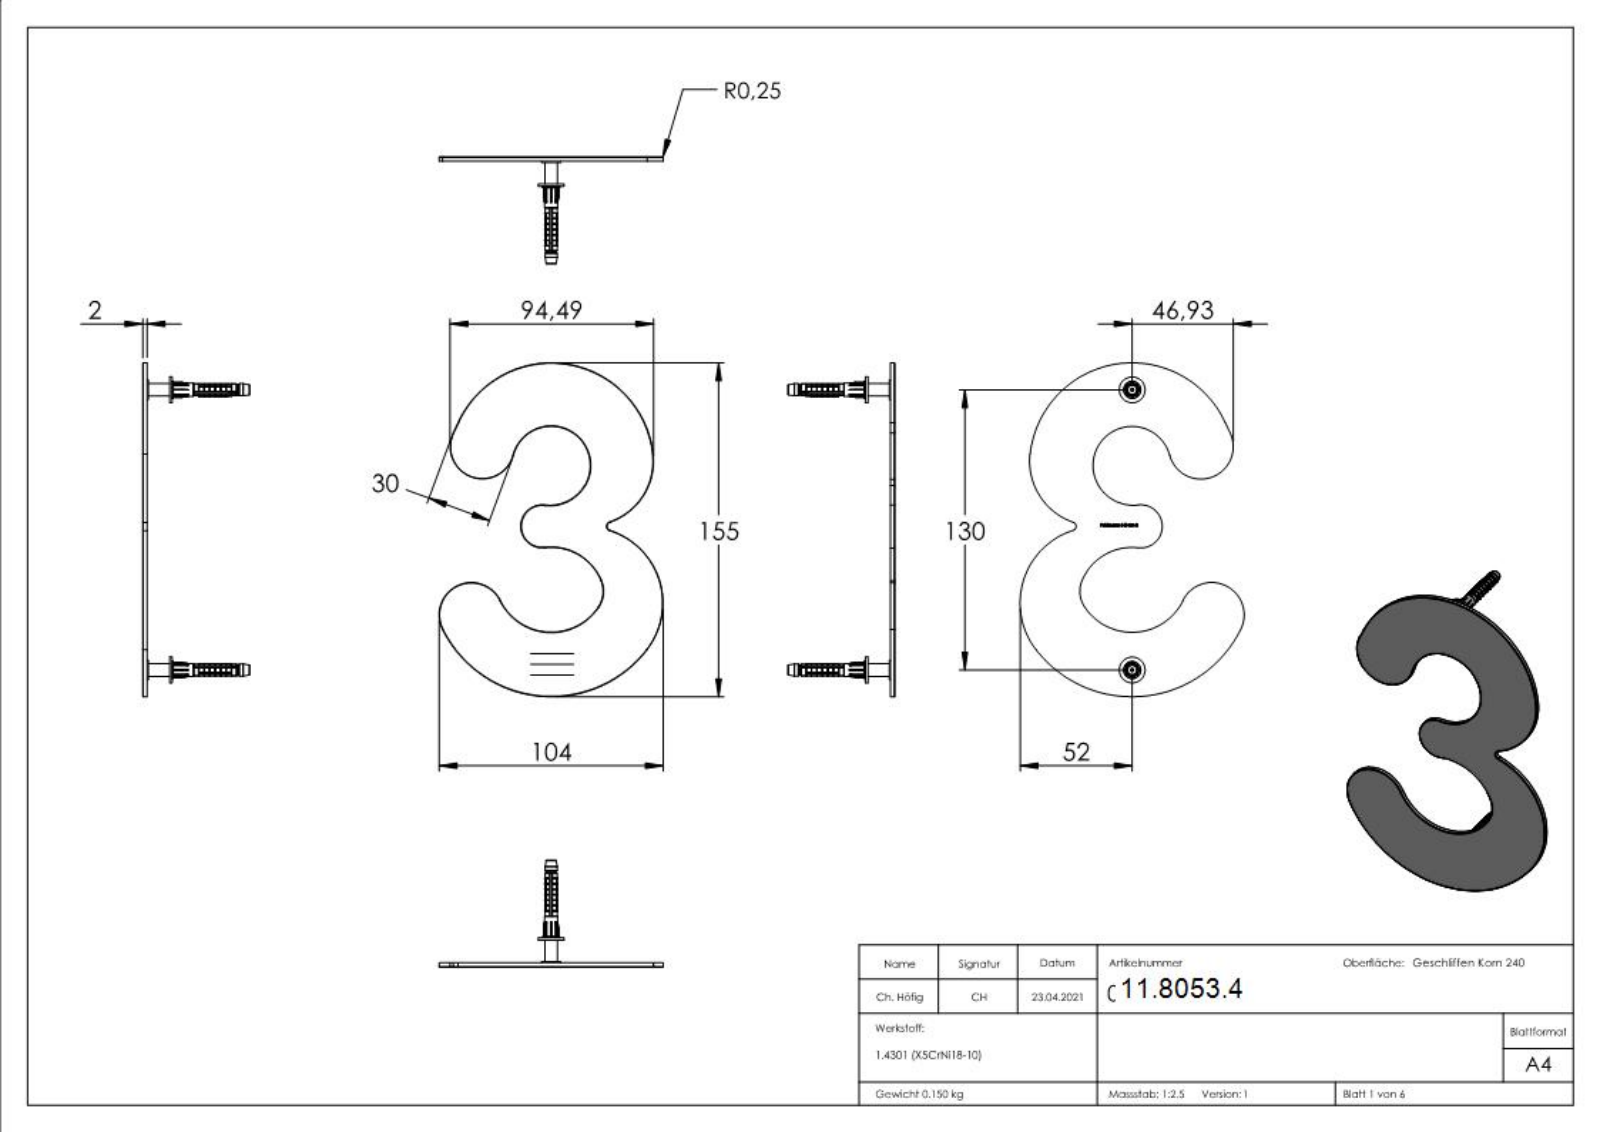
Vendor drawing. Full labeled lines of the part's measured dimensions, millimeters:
Part name (STEP PRODUCT): 040-HN-X Teil3; 040-HN-3; 040-HN-X Teil4_040-HN-X Teil4; 040-HN-X Teil1_040-HN-3 Teil1 (+5 more)
STEP written by: SolidWorks 2018 (CONFIG_CONTROL_DESIGN)
Units: millimetres
Bodies: 7 solids, 1574 faces (354 planar, 396 cylindrical, 824 other)
Overall size (bounding box): 10000 × 5217.43 × 4607.88
Volume: 19 895 mm³ · Surface area: 22 901 mm²
Round holes (diameter × count): ⌀3.3 ×2, ⌀4.3 ×2
Round bosses / shafts (diameter × count): ⌀12 ×2, ⌀9 ×2, ⌀8 ×2, ⌀6 ×2, ⌀5.8 ×2, ⌀5.6 ×2, ⌀4.6 ×2, ⌀4 ×2
Partial cylindrical surfaces — rounded edges, fillets, slot ends (radius × count): R0.1 ×22, R3.5 ×2, R15 ×2, R2 ×1, R10 ×1, R13 ×1, R18.12 ×1, R18.9 ×1
Main face-to-face distances: 2, 11.6, 13.6, 1.1, 10.5, 12.5, 1, 0.5, 2.5, 10
Hole centre spacings: 130
